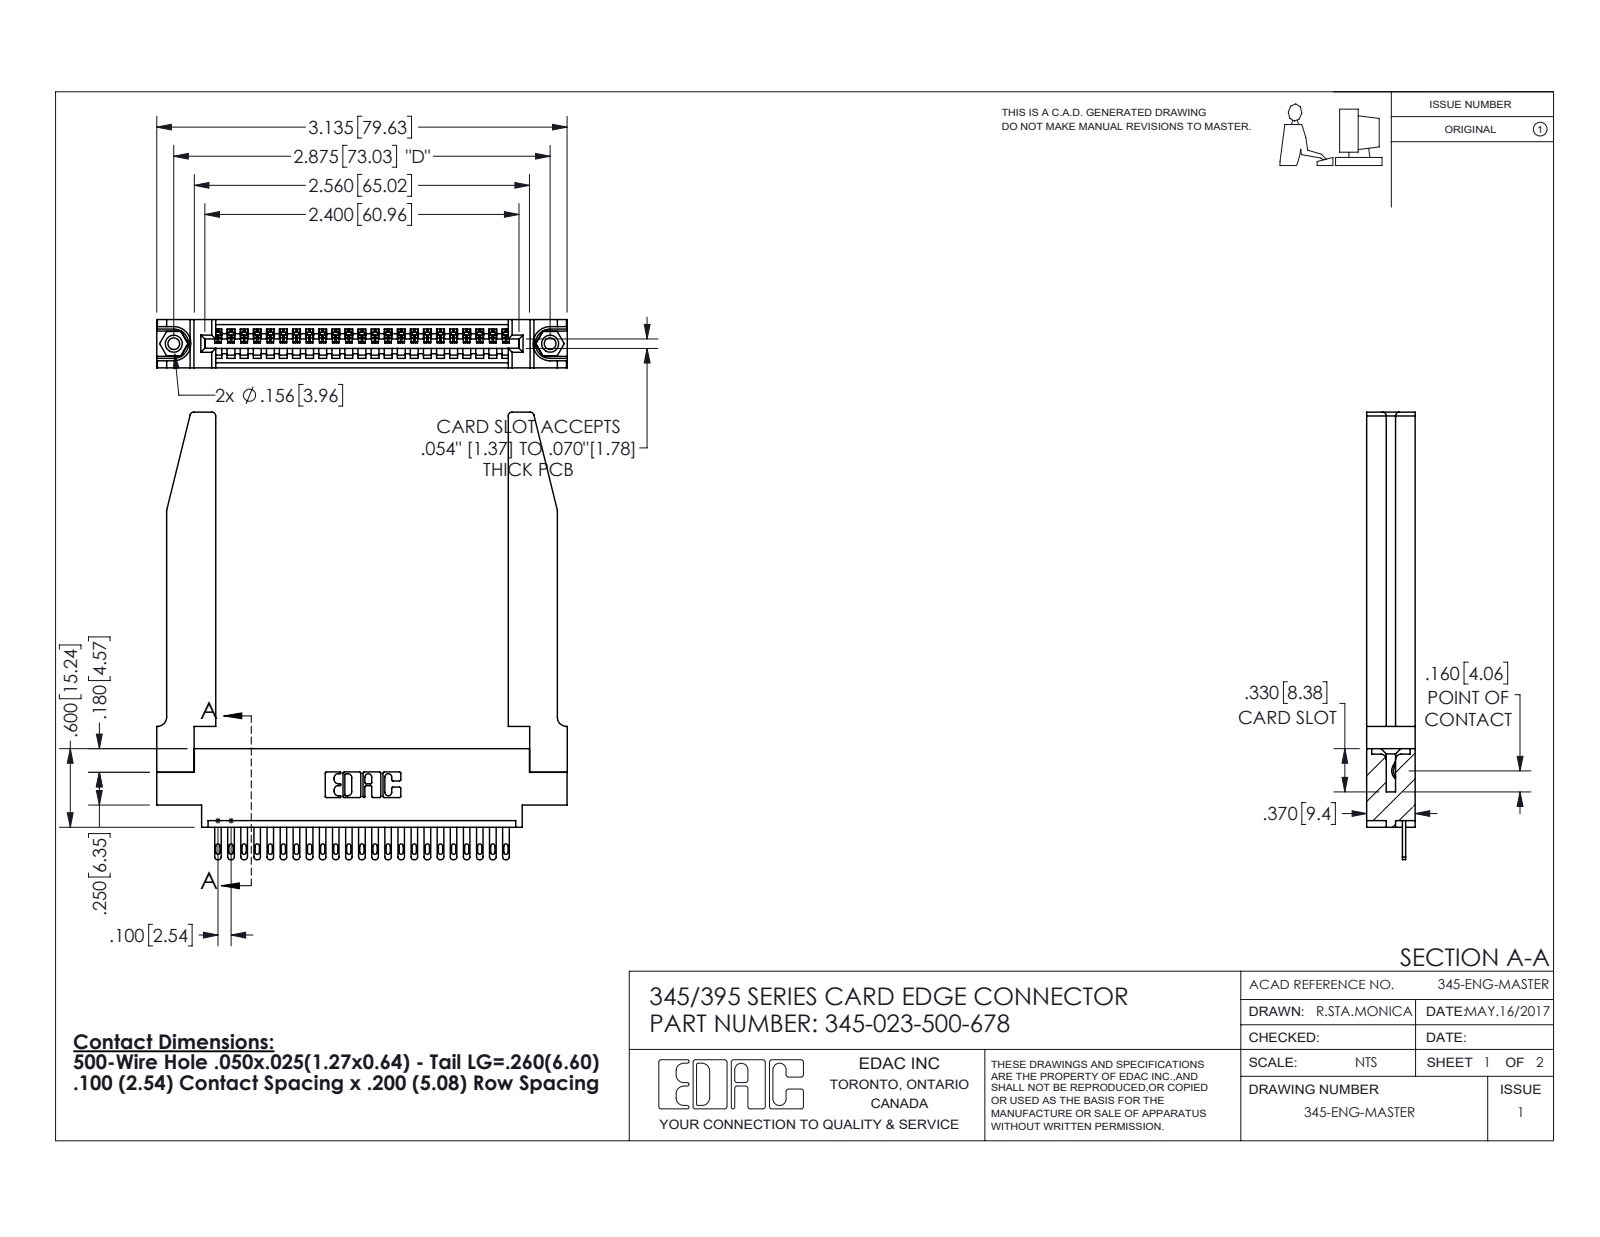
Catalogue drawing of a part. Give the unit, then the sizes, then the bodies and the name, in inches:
Units: inches
Overall size (bounding box): 3.417 × 3.136 × 0.37
Round holes (diameter × count): ⌀0.089 ×2, ⌀0.125 ×2, ⌀0.156 ×2, ⌀0.064 ×1
Round bosses / shafts (diameter × count): ⌀0.155 ×2
Partial cylindrical surfaces — rounded edges, fillets, slot ends (radius × count): R0.006 ×46, R0.016 ×46, R0.02 ×46, R0.01 ×22, R0.03 ×8, R0.007 ×6, R0.031 ×6, R0.026 ×3
Main face-to-face distances: 0.37, 0.072, 0.298, 0.098, 0.272, 0.025, 0.2, 0.148, 0.15, 0.123
Hole centre spacings: 0.27, 2.641, 2.875
Volume: 0.92 in³ · Surface area: 25.55 in²
Bodies: 28 solids, 1606 faces (1008 planar, 546 cylindrical, 52 other)
Part name (STEP PRODUCT): 345-250-001_345-250-001-102; 345-292-001_345-293-100; 345-220-078_345-220-078; 345 Part_0.170 Offset - 0.156 Dia-TH (+1 more)
STEP written by: SolidWorks 2016 (CONFIG_CONTROL_DESIGN)
